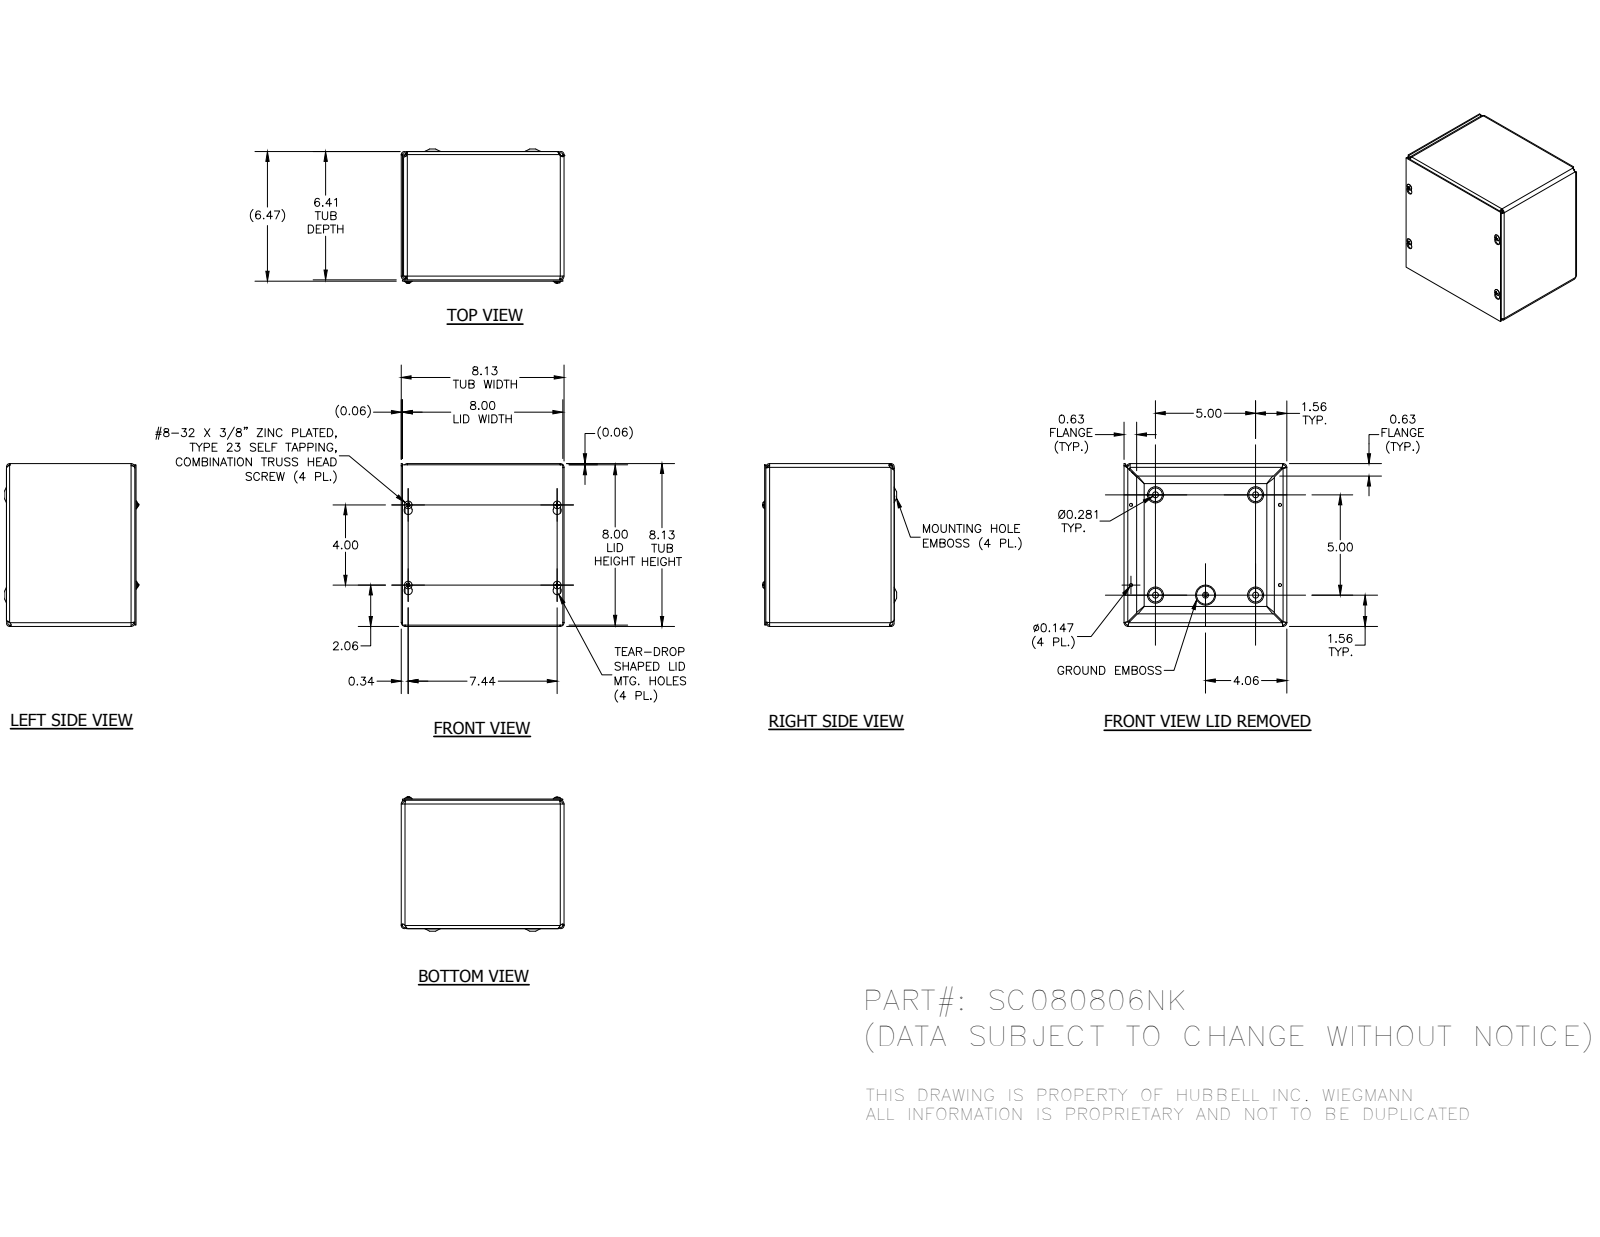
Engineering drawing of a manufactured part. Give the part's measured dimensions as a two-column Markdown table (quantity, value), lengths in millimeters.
| quantity | value |
| --- | --- |
| part name | SC0808BKP; SC080806NKWRA; SC0808LID; 34056 (+1 more) |
| STEP written by | Autodesk Inventor 2014 (AUTOMOTIVE_DESIGN) |
| units | millimeters |
| bodies | 7 solids, 357 faces (132 planar, 67 cylindrical, 158 other) |
| overall size | 206.38 × 206.38 × 170 |
| volume | 375 570 mm³ |
| surface area | 483 275 mm² |
| round holes (diameter × count) | 3.73 × 4, 7.62 × 4, 4.19 × 1 |
| round bosses / shafts (diameter × count) | 9.75 × 4, 4.17 × 4, 5.8 × 1 |
| partial cylindrical surfaces (radius × count) | 3.17 × 12, 4.75 × 8, 1.4 × 4, 1.57 × 4, 2.38 × 4, 2.97 × 4, 3.15 × 4, 3.96 × 4 |
| main face-to-face distances | 1.57, 204.8, 203.23, 161.12, 162.69, 1.58, 1.59, 162.71, 164.28, 206.37 |
| hole center spacings | 118.42, 127, 33.45, 33.46, 63.5, 101.6, 141.99, 158.46 |
